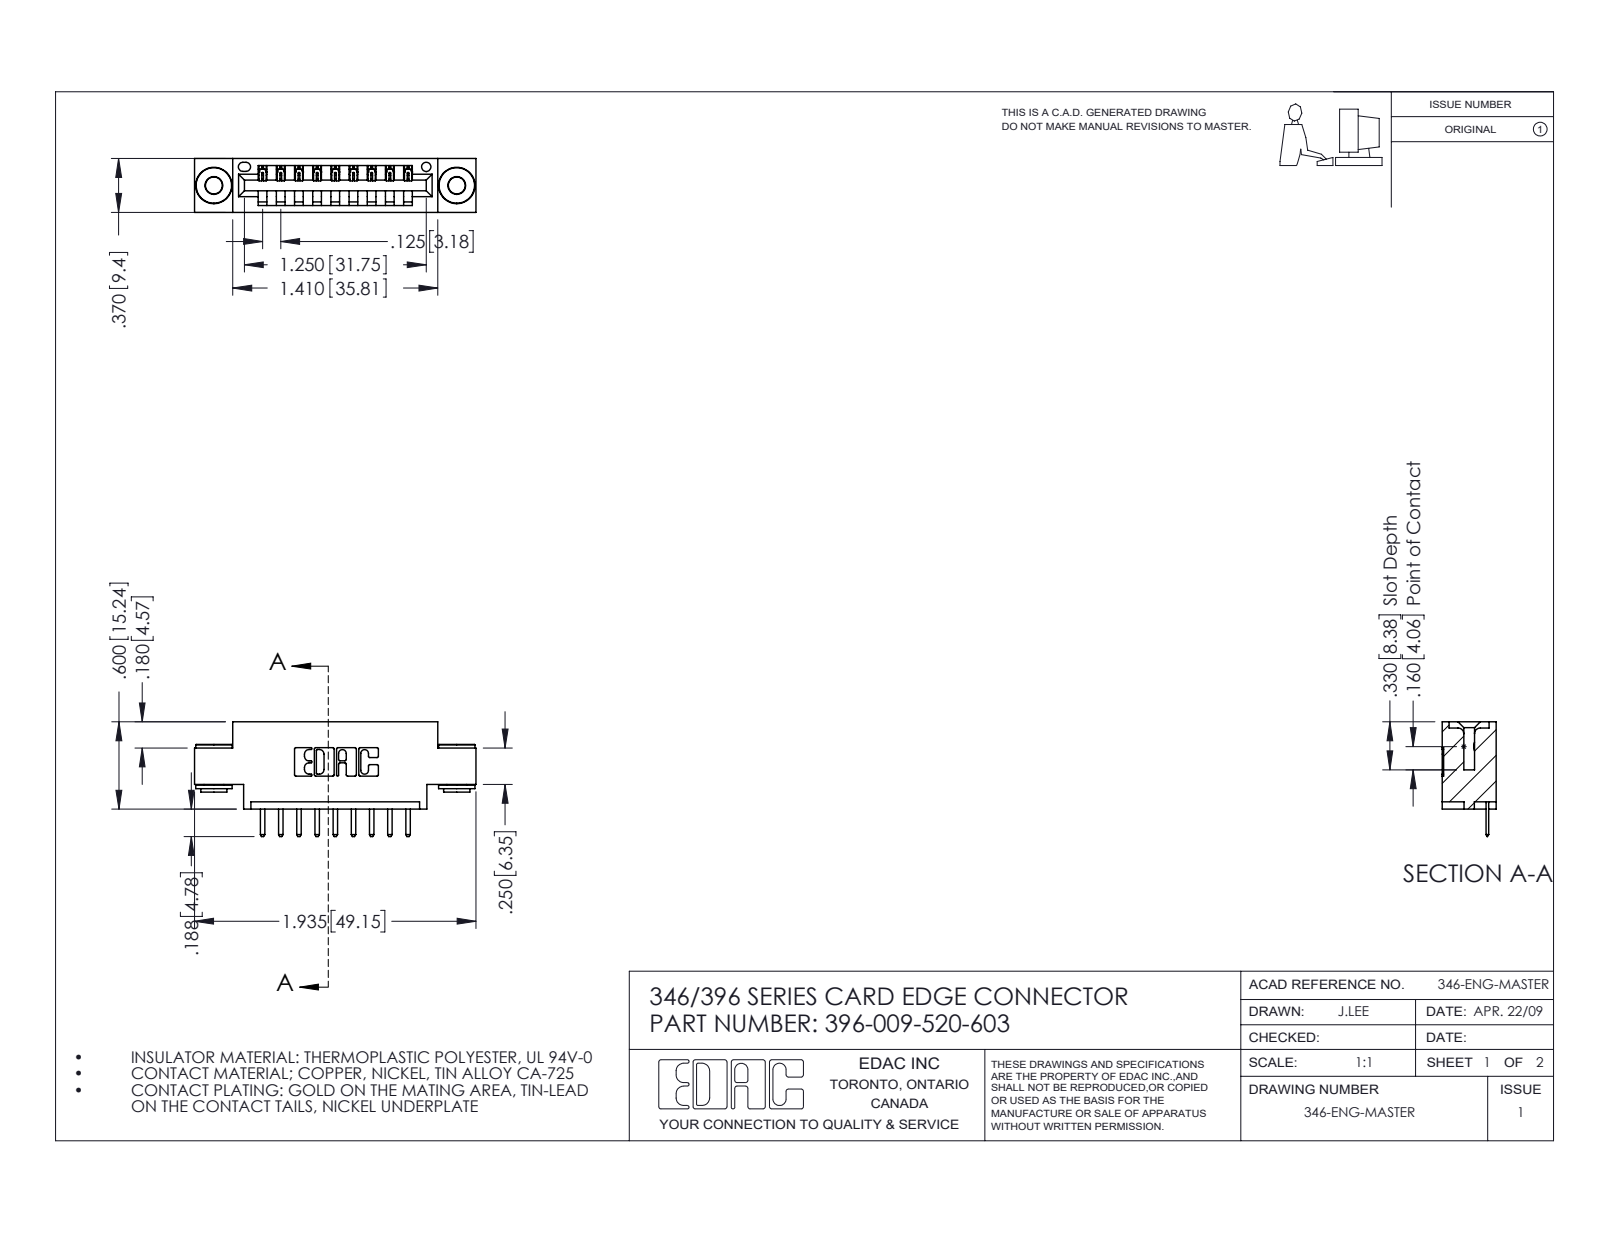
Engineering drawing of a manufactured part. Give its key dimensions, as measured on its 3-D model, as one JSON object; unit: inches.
{"part_name": "396-009-520-603; 346 Part_0.170 Offset - 0.156 Dia-TH; 345-250-002_345-250-002-102; 345-292-001_345-293-120", "step_written_by": "SolidWorks 2016 (CONFIG_CONTROL_DESIGN)", "units": "inches", "bodies": {"solids": 12, "faces": 722, "planar": 468, "cylindrical": 246, "other": 8}, "overall_size": [1.935, 0.788, 0.37], "volume_in3": 0.263, "surface_area_in2": 8.264, "round_holes": [[0.116, 2], [0.156, 2], [0.064, 1]], "round_bosses_or_shafts": [[0.25, 2], [0.18, 2], [0.136, 2]], "partial_cylinders_radius": [[0.01, 22], [0.01, 20], [0.006, 18], [0.007, 6], [0.031, 6], [0.026, 3], [0.031, 2], [0.04, 2]], "face_to_face_distances": [0.25, 0.37, 0.048, 0.322, 0.025, 0.148, 0.222, 0.1, 0.174, 0.275], "hole_center_spacings": [0.246, 1.465, 1.67]}
